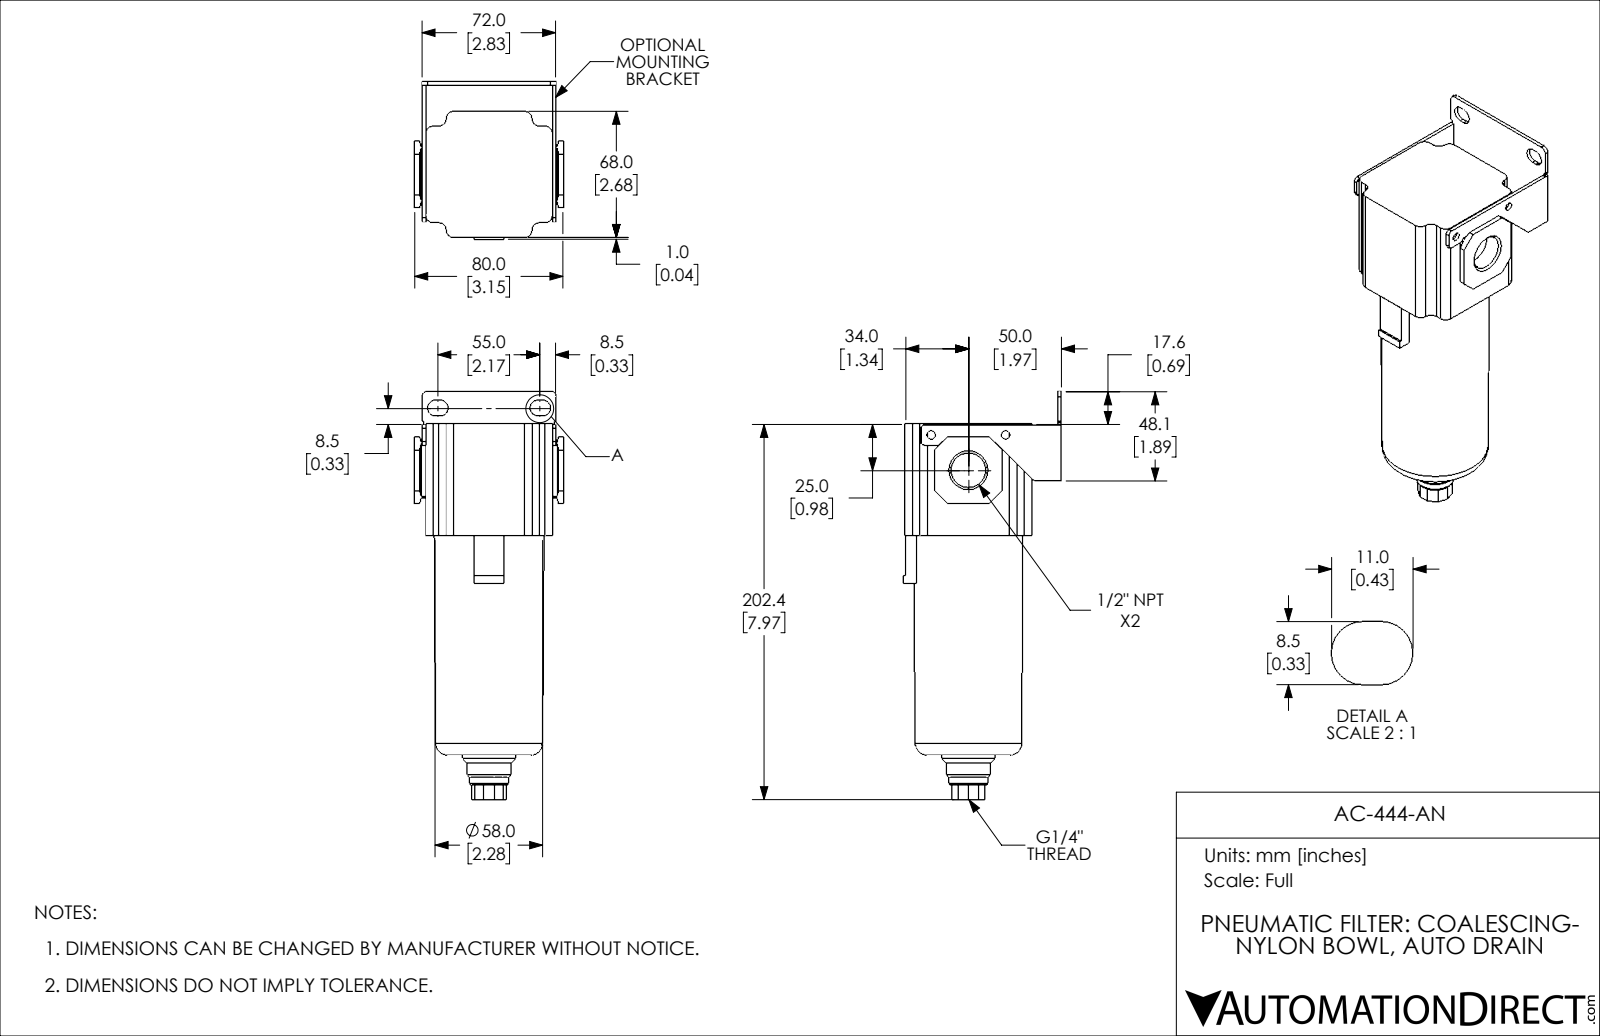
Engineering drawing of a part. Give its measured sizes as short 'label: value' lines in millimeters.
name: AC-444-AN
written by: SolidWorks 2018 (AUTOMOTIVE_DESIGN)
unit: mm
bodies: 1 solid, 166 faces (102 planar, 48 cylindrical, 16 other)
size: 220 × 85 × 80
volume: 586 800 mm³; area: 60 730 mm²
holes: 2× ⌀4.5, 1× ⌀11.5, 1× ⌀18.6
bosses: 1× ⌀28, 1× ⌀23, 1× ⌀20
rounds: 12× R4, 4× R4.2, 3× R2, 2× R1, 2× R3
face distances: 2, 68, 70, 16, 60, 84, 14, 82, 4, 6
hole spacings: 27.6, 40
